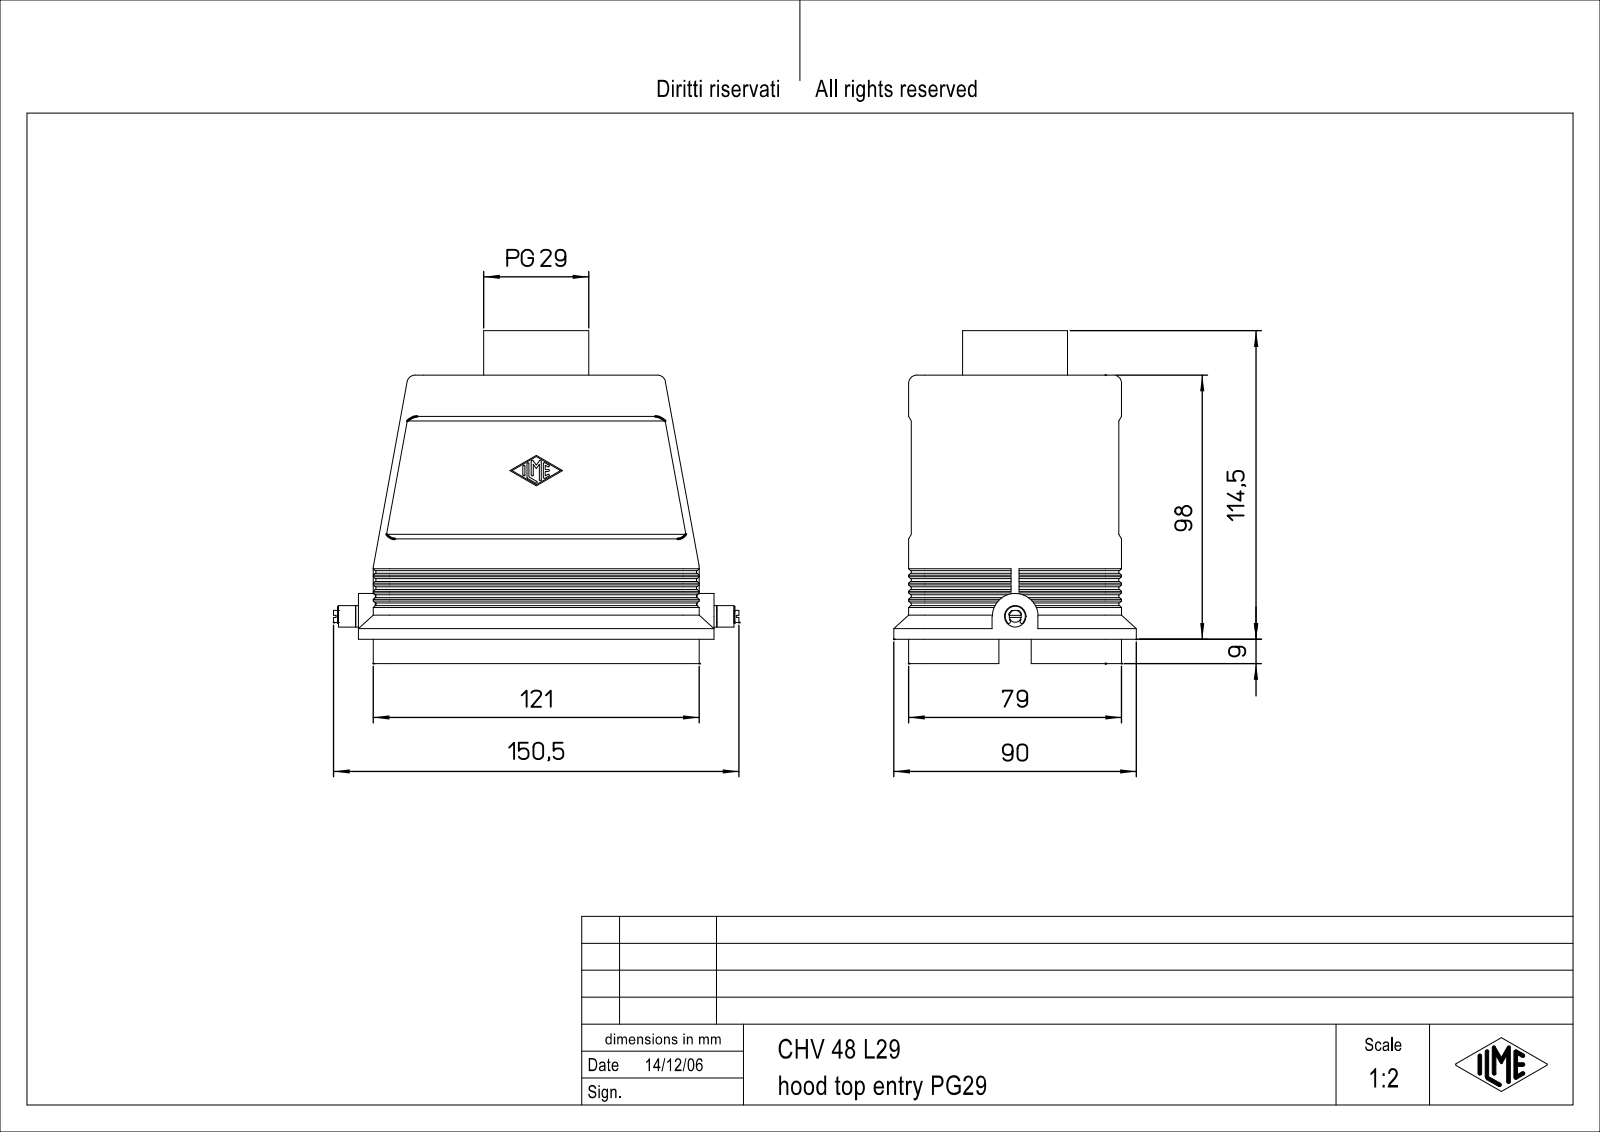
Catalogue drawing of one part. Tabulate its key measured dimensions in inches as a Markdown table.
| quantity | value |
| --- | --- |
| part name | CH_MH Tüllengehäuse Verschluss für 1 Bügel 104_62 Teil 2 |
| STEP written by | Autodesk Inventor 7 (AUTOMOTIVE_DESIGN) |
| units | inches |
| bodies | 1 solid, 686 faces (250 planar, 185 cylindrical, 251 other) |
| overall size | 5.925 × 5 × 3.543 |
| volume | 14.47 in³ |
| surface area | 172.1 in² |
| round holes (diameter × count) | 0.097 × 4, 0.138 × 4, 1.318 × 1, 1.397 × 1, 1.85 × 1 |
| round bosses / shafts (diameter × count) | 1.811 × 1, 1.575 × 1, 1.515 × 1, 0.315 × 1, 0.236 × 1, 0.177 × 1, 0.138 × 1 |
| partial cylindrical surfaces (radius × count) | 0.015 × 14, 0.079 × 12, 0.236 × 10, 0.02 × 4, 0.118 × 4, 0.453 × 4, 0.037 × 3, 0.024 × 2 |
| main face-to-face distances | 0.138, 2.835, 2.972, 0.039, 0.394, 4.291, 0.098, 3.11, 2.933, 3.071 |
| hole center spacings | 1.063, 2.053, 2.383, 4.094, 4.23 |
